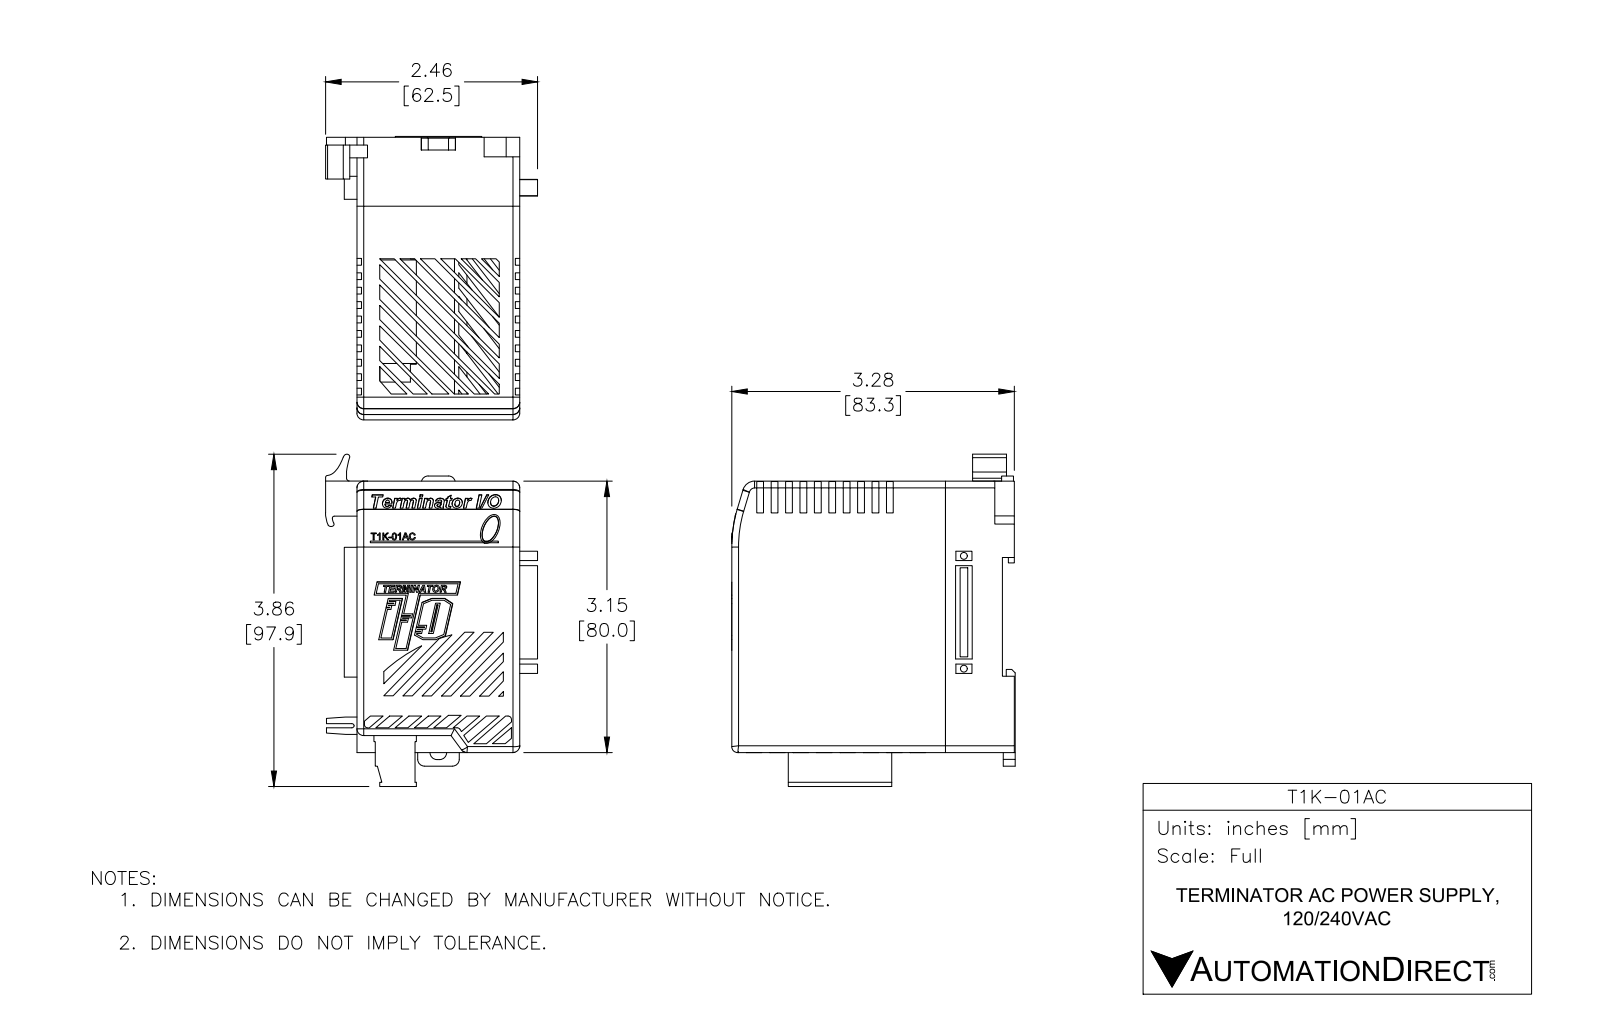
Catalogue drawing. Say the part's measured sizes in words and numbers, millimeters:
The part is named "Terminator_AC_PwrSupply With LOGO_with venting". Its 3-D file was written by "SolidWorks 2013 (AUTOMOTIVE_DESIGN)". It is 18 solids with 914 faces: 681 planar, 66 cylindrical and 167 other. Overall it measures 97.96 by 83.59 by 62.5 millimeters. Its volume is 109 263 cubic millimeters and its surface area 56 851 square millimeters. Round holes: 2 of diameter 2. Round bosses or shafts: 2 of diameter 1.81. Partial cylindrical surfaces (rounded edges, fillets, slot ends): 18 of radius 2, 12 of radius 1, 4 of radius 0.75, 2 of radius 2.06, 1 of radius 0.83, 1 of radius 0.94, 1 of radius 2.02, 1 of radius 2.04. The main face-to-face distances are 2, 46, 48, 44, 63, 61, 3.5, 16.8, 77.8, 79.8. The hole center spacings are 33.25.
